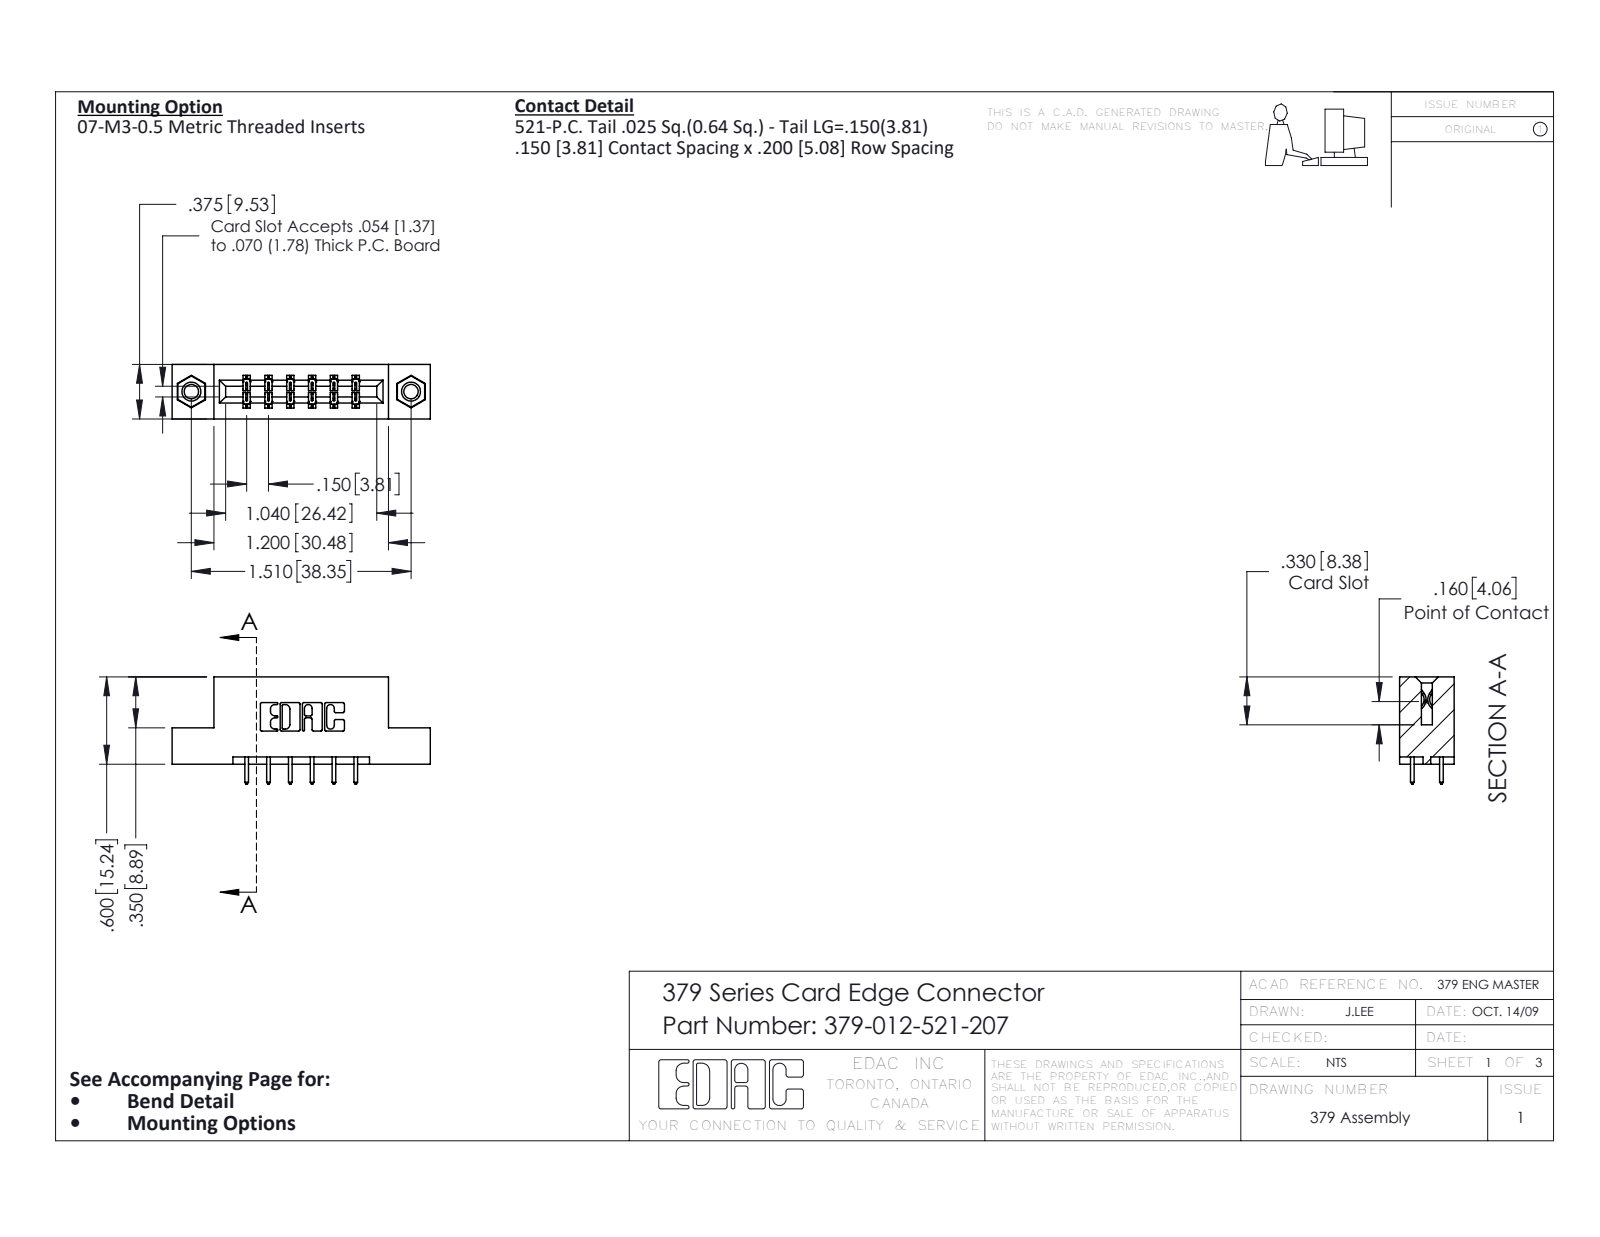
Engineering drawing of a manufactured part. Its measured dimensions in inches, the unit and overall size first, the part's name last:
Units: inches
Overall size (bounding box): 1.775 × 0.737 × 0.375
Round holes (diameter × count): ⌀0.098 ×2, ⌀0.125 ×2, ⌀0.156 ×2
Round bosses / shafts (diameter × count): ⌀0.155 ×2
Partial cylindrical surfaces — rounded edges, fillets, slot ends (radius × count): R0.01 ×22, R0.006 ×18, R0.01 ×12, R0.007 ×6, R0.031 ×6, R0.026 ×3, R0.014 ×2, R0.022 ×2
Main face-to-face distances: 0.3, 0.2, 0.05, 0.15, 0.375, 0.1, 0.25, 0.35, 0.075, 0.55
Hole centre spacings: 1.51
Volume: 0.264 in³ · Surface area: 7.024 in²
Bodies: 15 solids, 798 faces (534 planar, 248 cylindrical, 16 other)
Part name (STEP PRODUCT): 379-012-521-207; 345-250-001_345-250-005-103; 345-292-001_345-293-121; 379 Part_Flush - .156 Dia - TI
STEP written by: SolidWorks 2016 (CONFIG_CONTROL_DESIGN)
